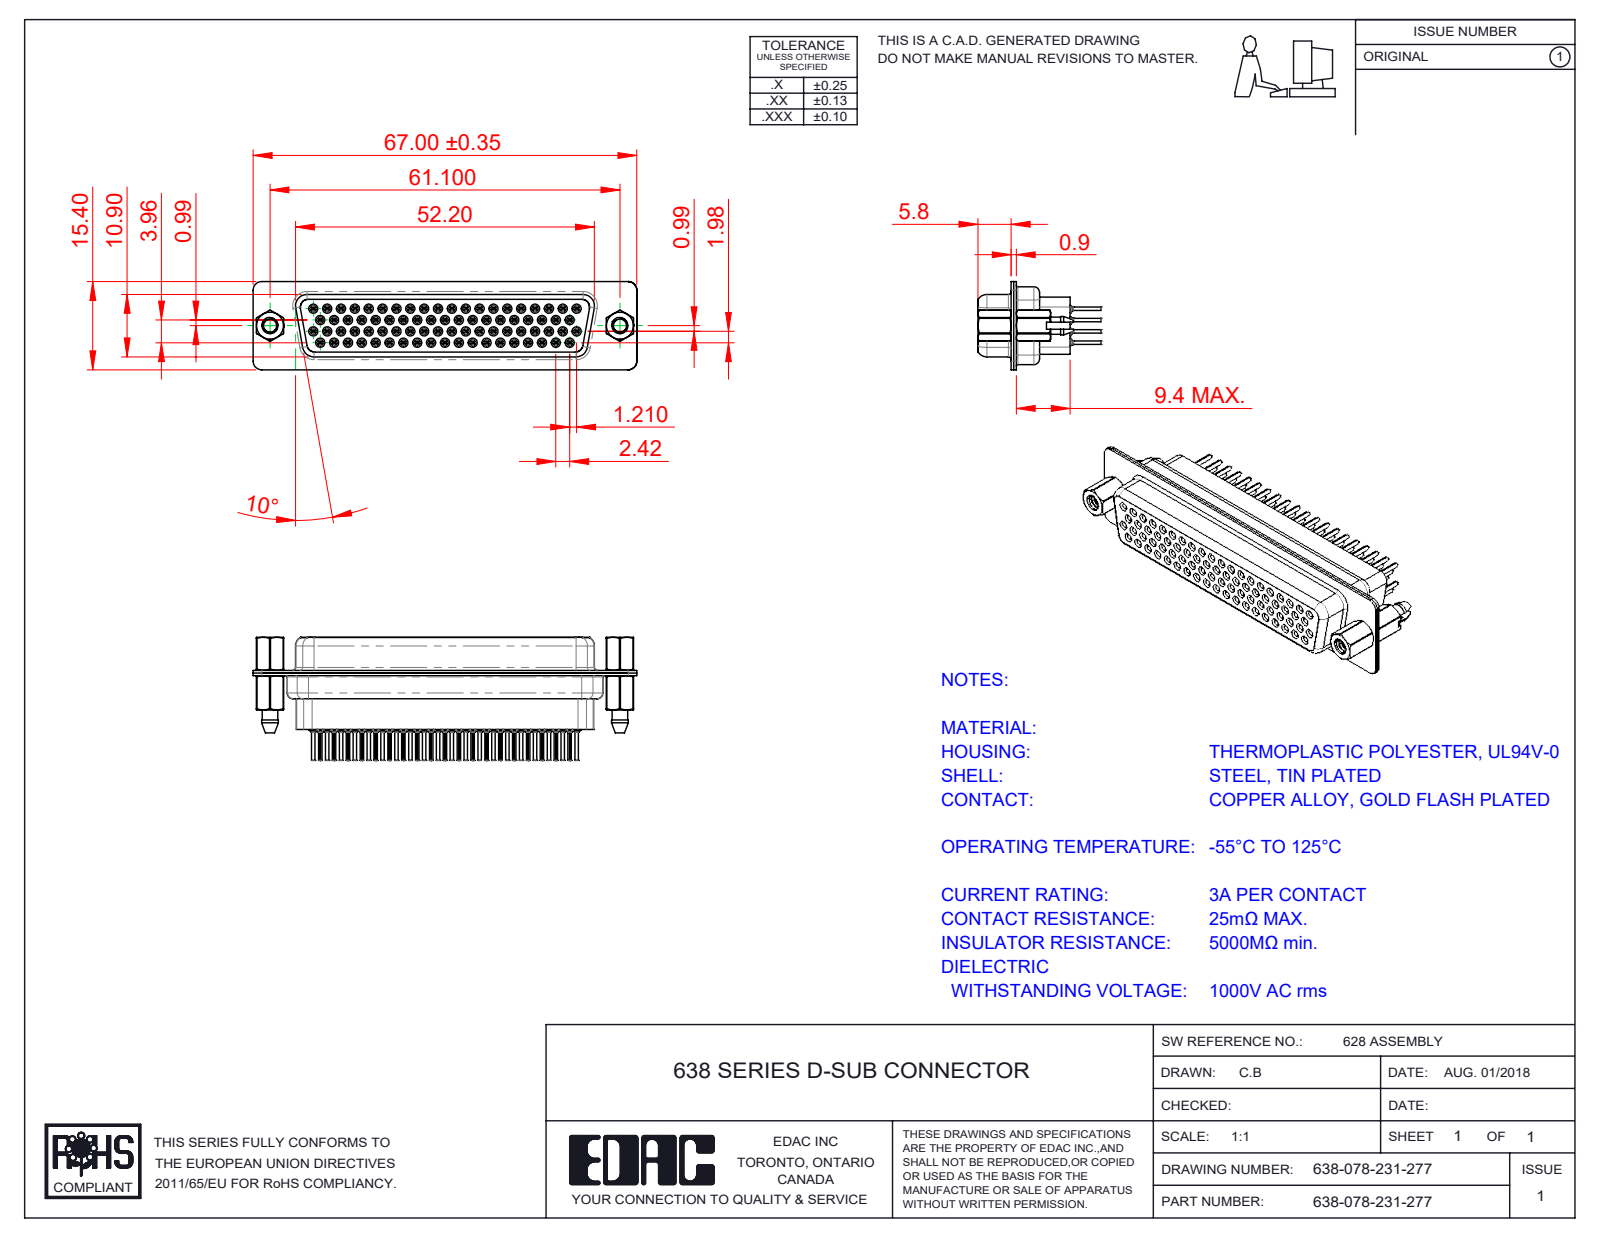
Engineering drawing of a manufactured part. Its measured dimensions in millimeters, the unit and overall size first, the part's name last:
Units: millimetres
Overall size (bounding box): 67 × 21.5 × 15.4
Round holes (diameter × count): ⌀0.2 ×78, ⌀0.8 ×78, ⌀1 ×78, ⌀1.1 ×78, ⌀1.6 ×78, ⌀1.7 ×78, ⌀1.8 ×78, ⌀2.26 ×2, ⌀2.29 ×2, ⌀4 ×2, ⌀4.05 ×2, ⌀4.85 ×2
Round bosses / shafts (diameter × count): ⌀2 ×78, ⌀1.5 ×78, ⌀1.2 ×78, ⌀0.6 ×78, ⌀4.95 ×2, ⌀4.8 ×2, ⌀2.79 ×2, ⌀4 ×1
Partial cylindrical surfaces — rounded edges, fillets, slot ends (radius × count): R0.1 ×156, R0.28 ×39, R1.5 ×18, R2 ×12, R1.55 ×8, R0.25 ×4, R0.5 ×4, R0.55 ×4
Main face-to-face distances: 0.45, 0.4, 9.6, 0.9, 1.35, 11.8, 11.4, 1.8, 10, 10.3
Hole centre spacings: 2.42, 4.84, 7.26, 9.68, 6.06, 12.1, 6.96, 8.48
Volume: 7 635 mm³ · Surface area: 25 781 mm²
Bodies: 85 solids, 10073 faces (2539 planar, 2815 cylindrical, 4719 other)
Part name (STEP PRODUCT): 638 Contact Row 3_31; 638 Shell Front_78 Contacts; 638 Housing_78 Contacts HP; 638 Contact Row 1_31 (+6 more)
STEP written by: SolidWorks 2020 (CONFIG_CONTROL_DESIGN)
